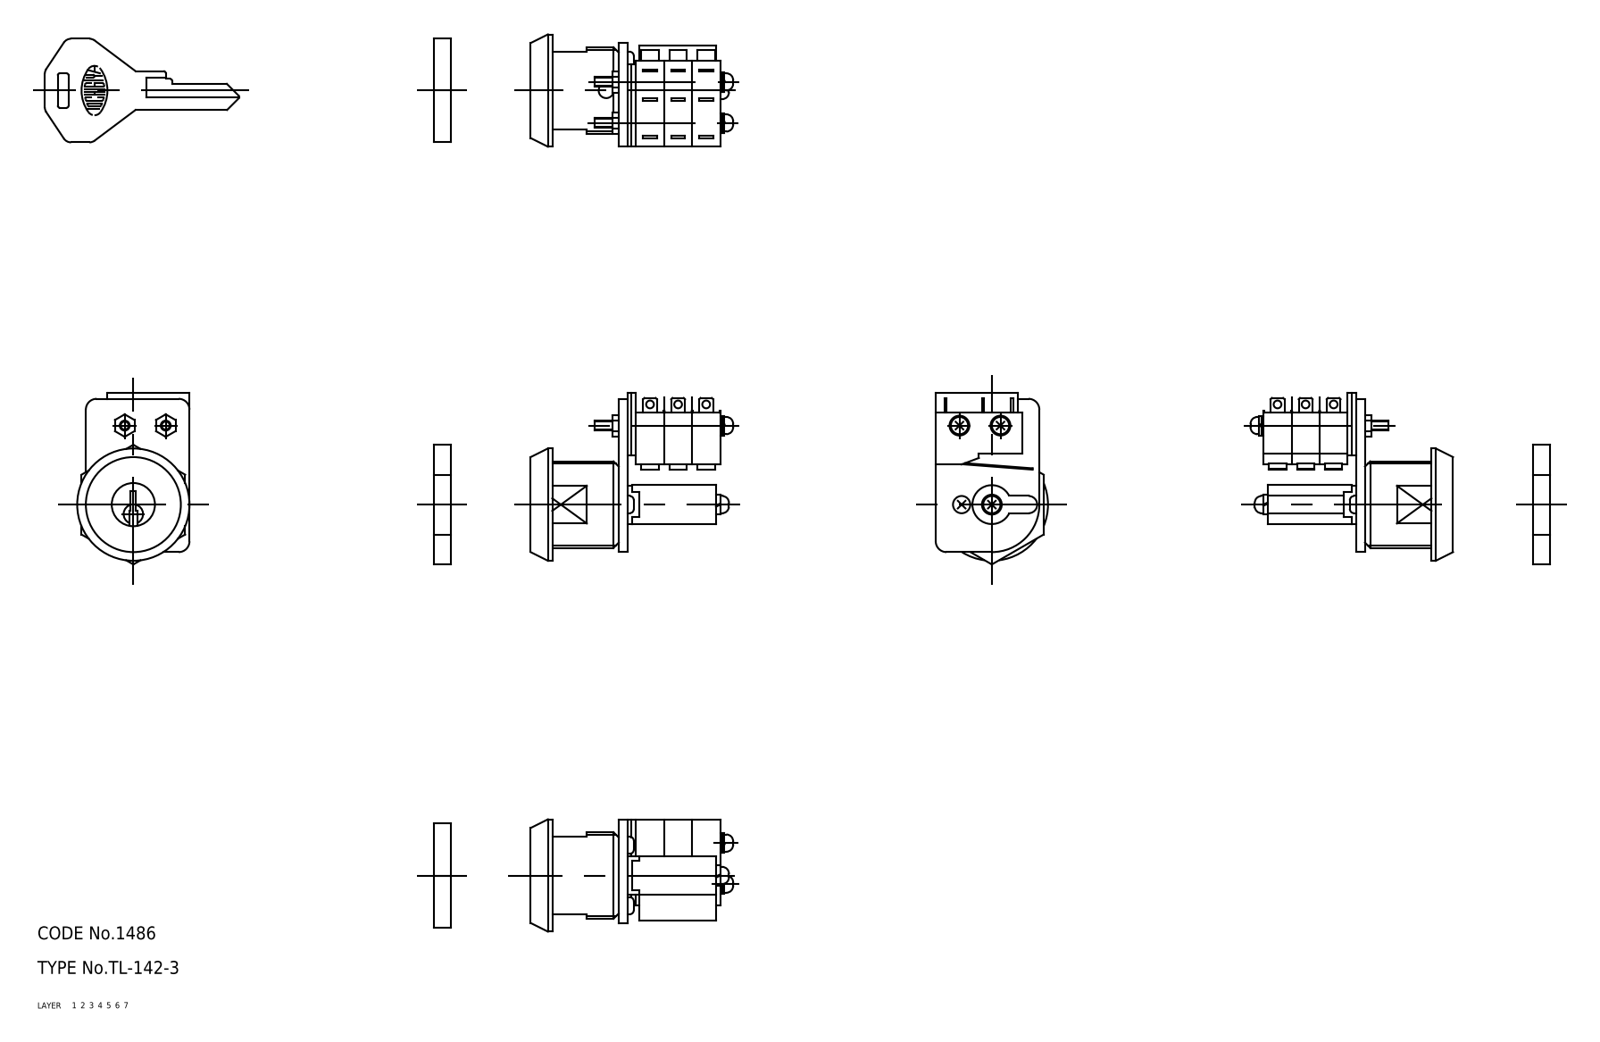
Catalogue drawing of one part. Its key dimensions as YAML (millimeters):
part_name: "switch; spacer_B; screw_3; nut_3 (+8 more)"
step_written_by: "CADfix (AUTOMOTIVE_DESIGN)"
units: millimeters
bodies: {solids: 19, faces: 467, planar: 0, cylindrical: 0, other: 467}
overall_size: [120.41, 39.66, 26]
volume: 16475
surface_area: 14928
